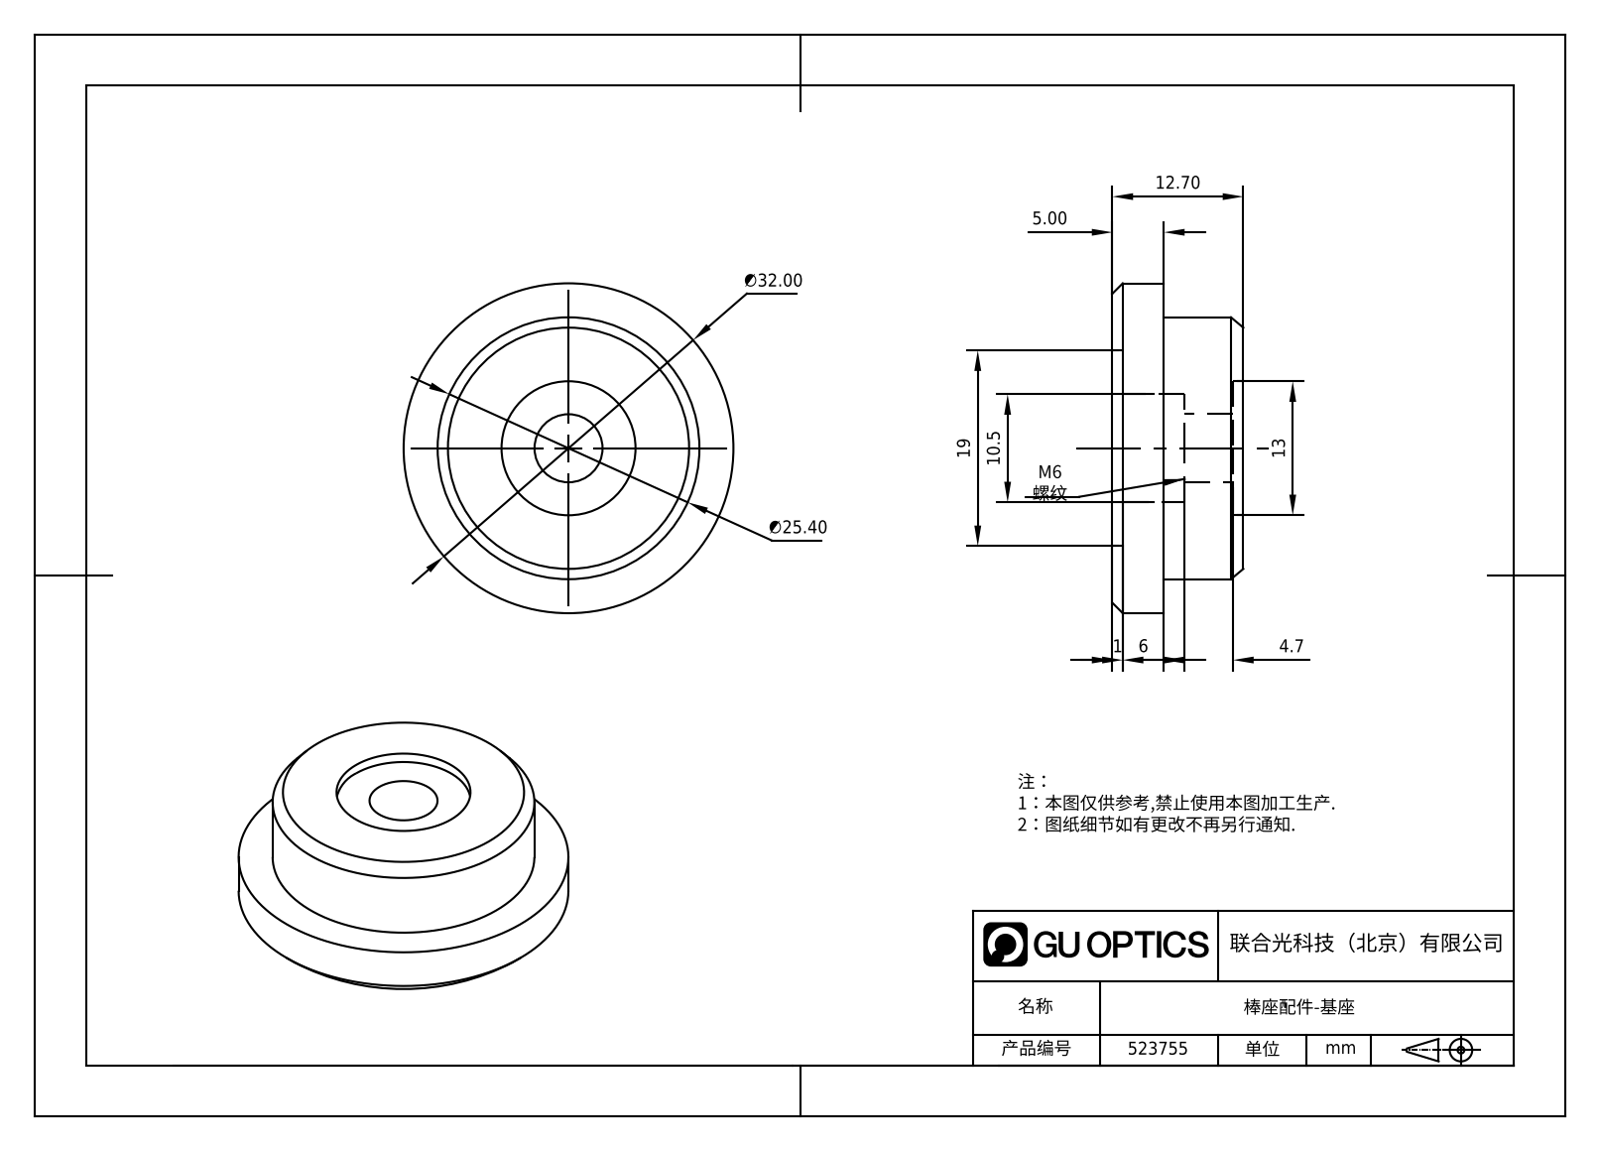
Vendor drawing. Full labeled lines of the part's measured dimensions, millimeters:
Part name (STEP PRODUCT): 523755
STEP written by: SolidWorks 2020 (CONFIG_CONTROL_DESIGN)
Units: millimetres
Bodies: 1 solid, 14 faces (6 planar, 6 cylindrical, 2 other)
Overall size (bounding box): 32 × 32 × 12.7
Volume: 6 730 mm³ · Surface area: 2 940 mm²
Round holes (diameter × count): ⌀6.6 ×1, ⌀10.5 ×1, ⌀13 ×1, ⌀19 ×1
Round bosses / shafts (diameter × count): ⌀32 ×1, ⌀25.4 ×1
Main face-to-face distances: 5, 12.7, 7.7, 1, 11.7, 4, 10.7, 6.7, 7, 6
